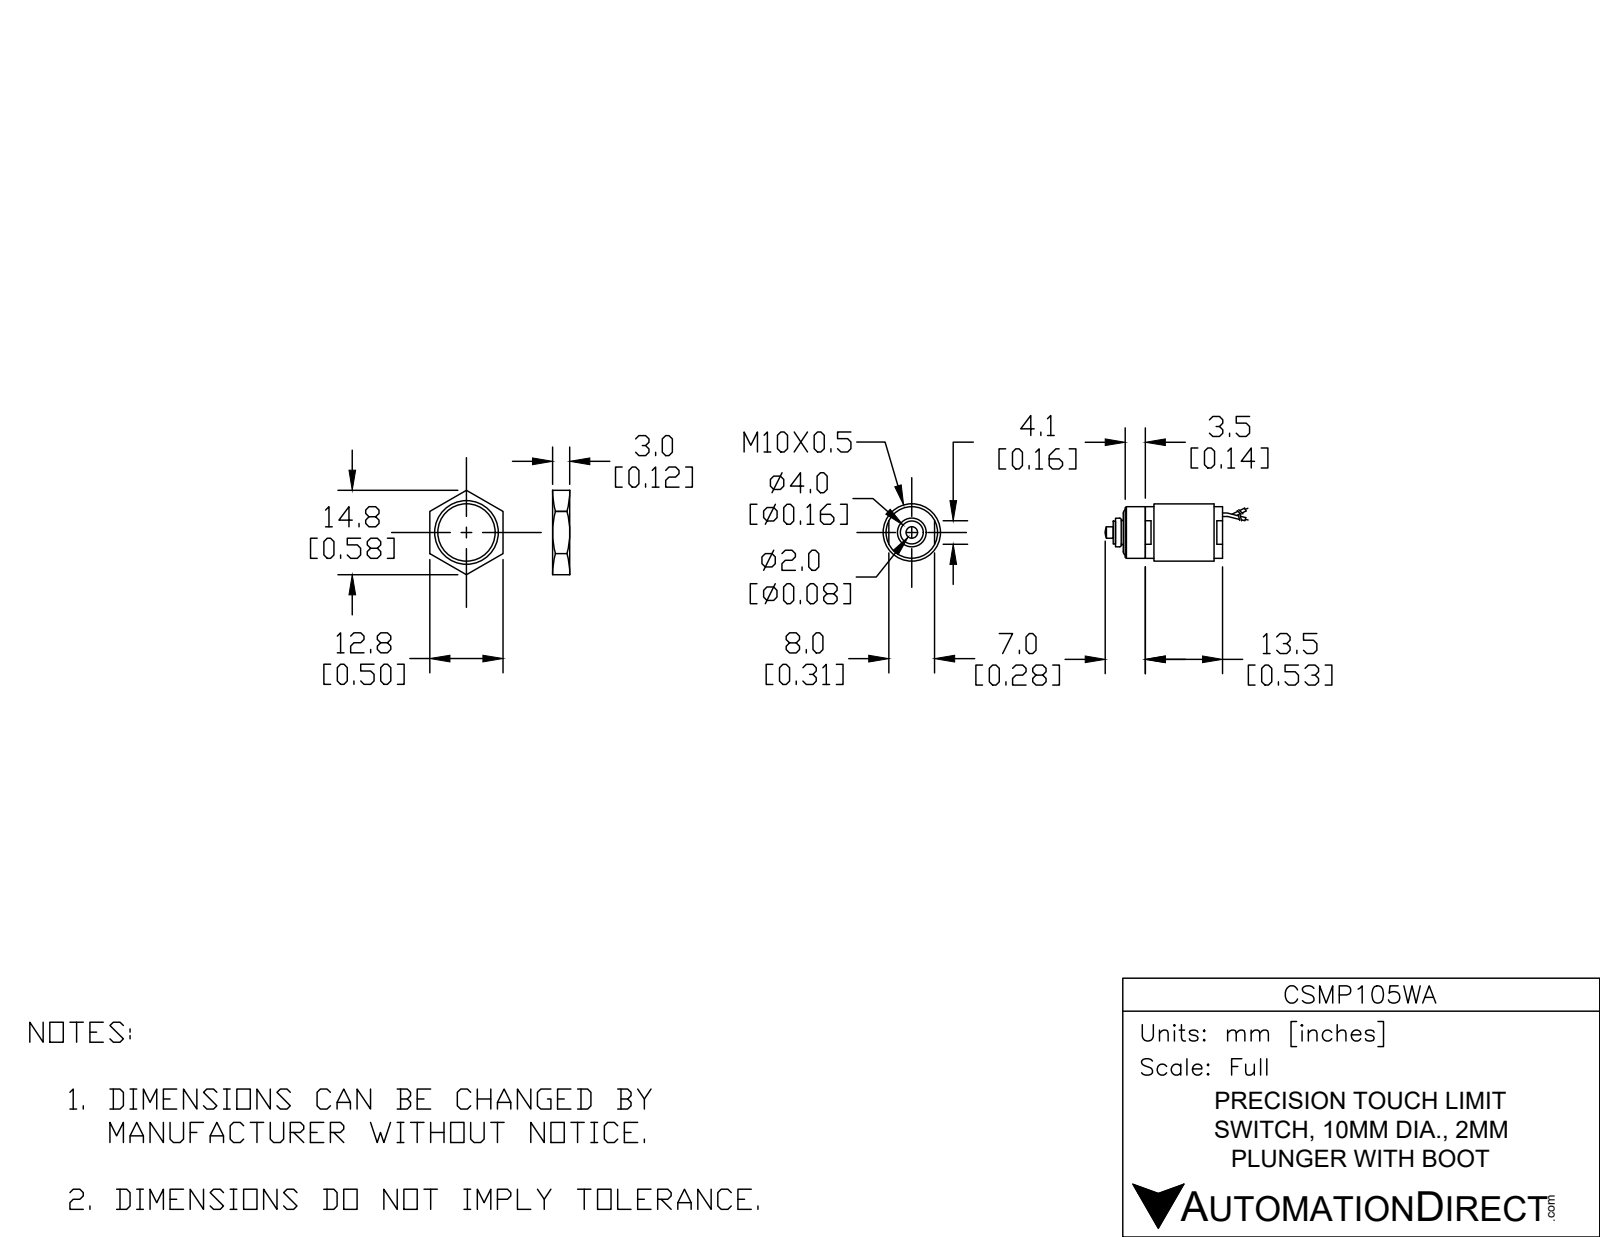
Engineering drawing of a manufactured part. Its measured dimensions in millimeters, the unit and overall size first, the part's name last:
Units: millimetres
Overall size (bounding box): 25.5 × 10 × 10
Round bosses / shafts (diameter × count): ⌀0.6 ×2, ⌀10 ×1, ⌀9 ×1, ⌀5 ×1, ⌀4 ×1, ⌀2 ×1
Main face-to-face distances: 17.35, 1.5, 12, 0.35, 15.85, 5.35, 10.5, 1.75, 7.1, 17.6
Volume: 1 229 mm³ · Surface area: 970 mm²
Bodies: 1 solid, 92 faces (20 planar, 57 cylindrical, 15 other)
Part name (STEP PRODUCT): CSMP105WA
STEP written by: SolidWorks 2016 (CONFIG_CONTROL_DESIGN)
